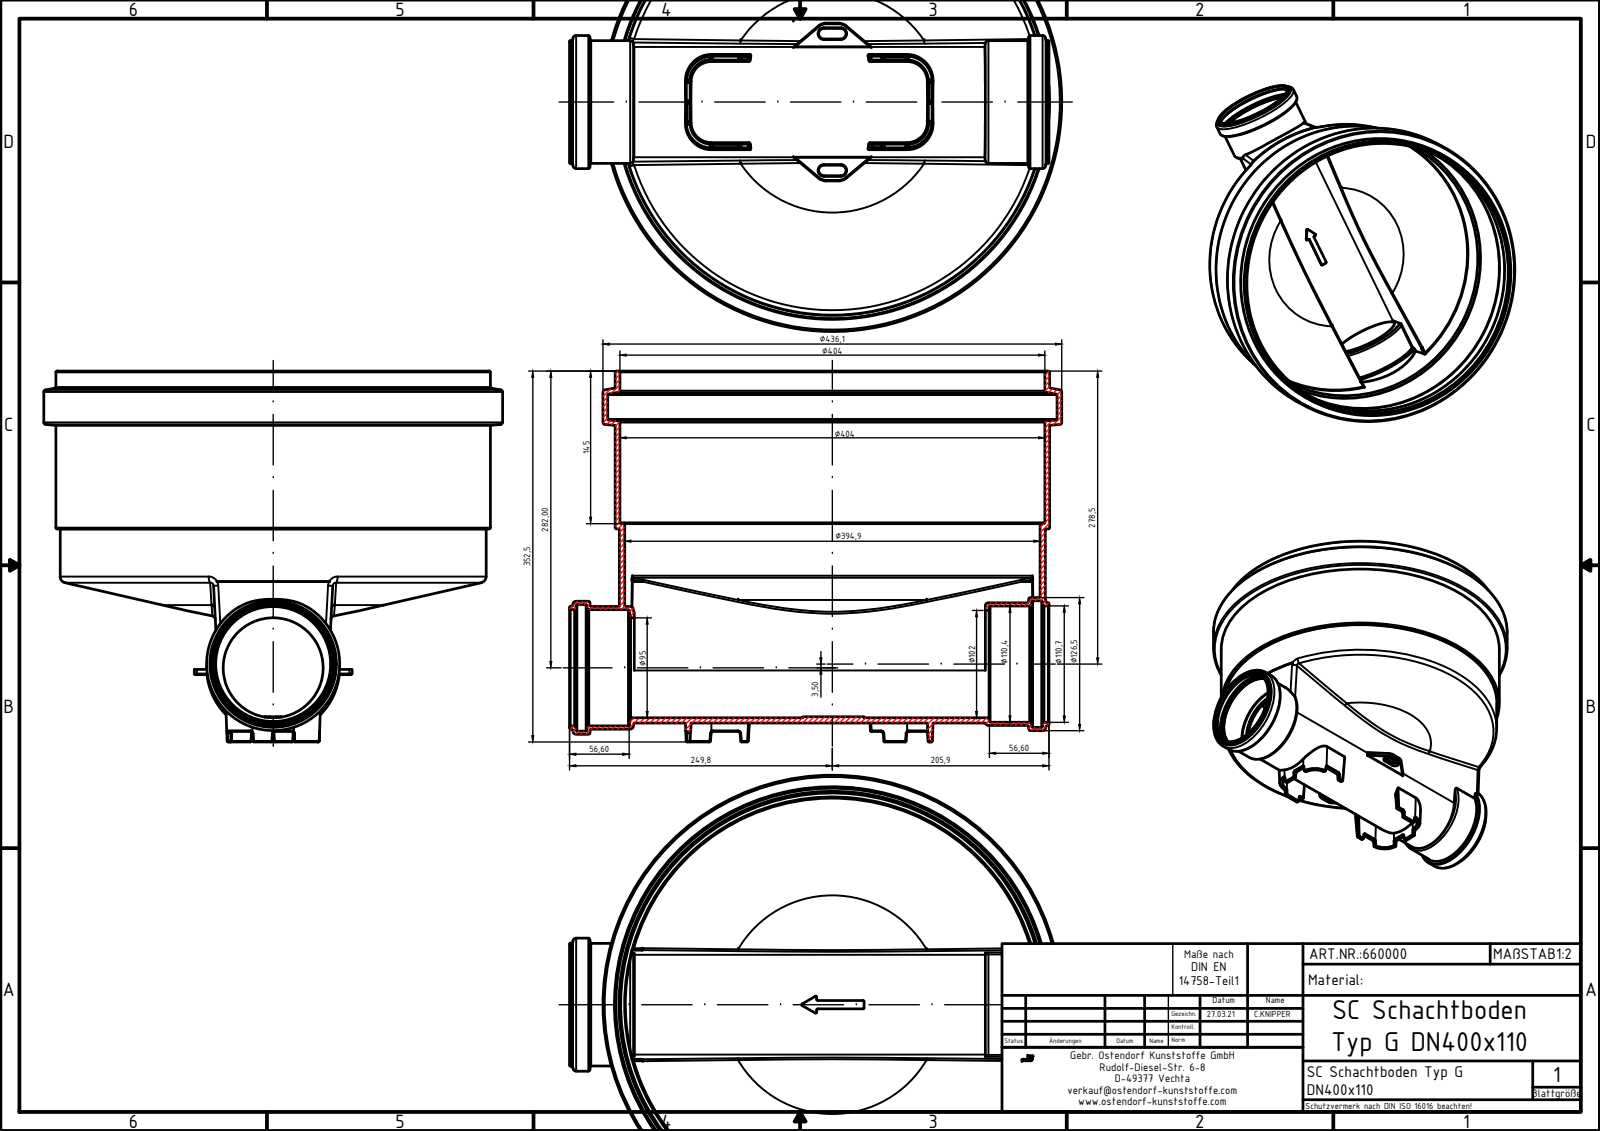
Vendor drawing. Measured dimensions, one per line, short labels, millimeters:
name: 660000 SC Schachtboden Typ G DN400_110
written by: Autodesk Inventor 2020 (AUTOMOTIVE_DESIGN)
unit: mm
bodies: 1 solid, 503 faces (85 planar, 138 cylindrical, 280 other)
size: 467.85 × 436.1 × 352.5
volume: 2 505 000 mm³; area: 1 078 000 mm²
holes: 2× ⌀110.4, 2× ⌀110.7, 2× ⌀120.3, 1× ⌀95, 1× ⌀102, 1× ⌀394.9, 1× ⌀404, 1× ⌀427.1
bosses: 2× ⌀126.5, 2× ⌀116.9, 2× ⌀116.6, 1× ⌀436.1, 1× ⌀413, 1× ⌀404.9, 1× ⌀105
rounds: 73× R1, 16× R2, 4× R5, 4× R11
face distances: 5, 83.41, 138.5, 145, 150, 133.5, 283.5, 143.5, 288.5, 229.77
hole spacings: 3.5
